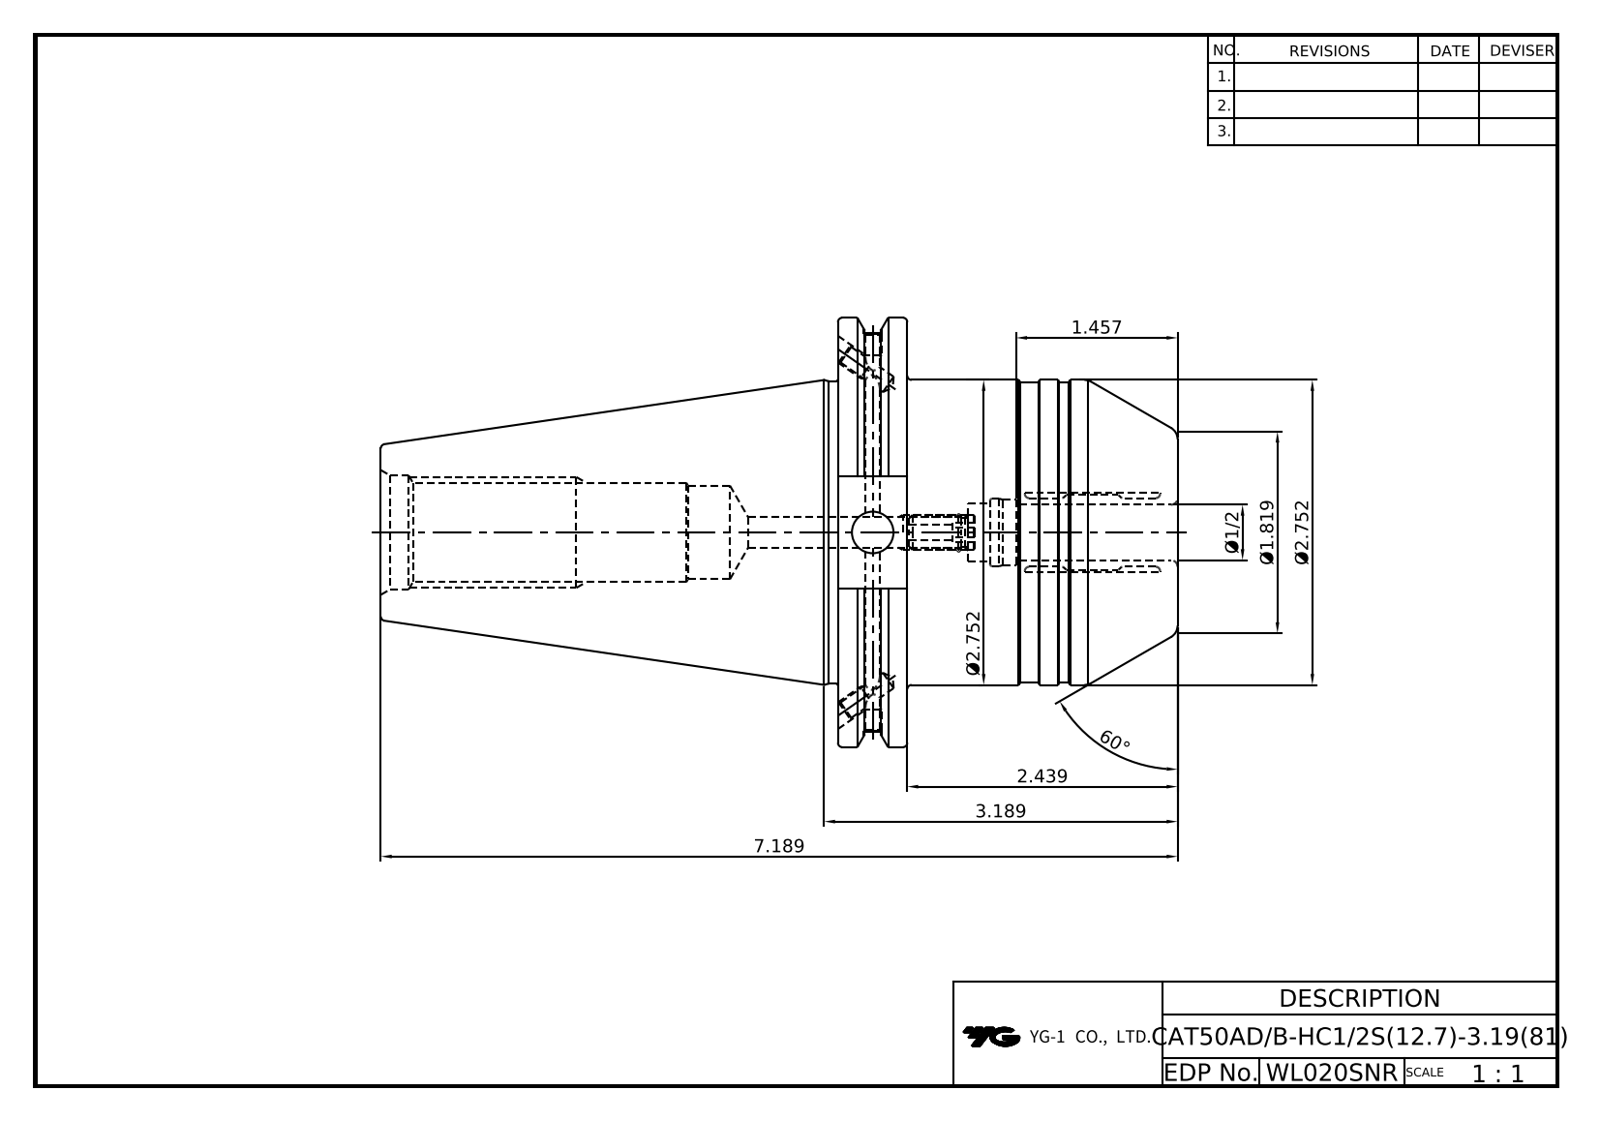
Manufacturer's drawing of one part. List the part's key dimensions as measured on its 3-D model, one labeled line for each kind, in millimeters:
Part name (STEP PRODUCT): LO-CAT50ADB-HC12.7S-81
STEP written by: Autodesk Inventor 2020 (AUTOMOTIVE_DESIGN)
Units: millimetres
Bodies: 1 solid, 102 faces (37 planar, 31 cylindrical, 34 other)
Overall size (bounding box): 182.6 × 98.42 × 94.69
Volume: 537 821 mm³ · Surface area: 57 060 mm²
Round holes (diameter × count): ⌀3.24 ×2, ⌀4.13 ×2, ⌀4.2 ×2, ⌀5 ×2, ⌀6.92 ×1, ⌀9.53 ×1, ⌀12.7 ×1, ⌀13.2 ×1, ⌀21.5 ×1, ⌀21.97 ×1, ⌀26.2 ×1
Round bosses / shafts (diameter × count): ⌀98.42 ×1, ⌀91.29 ×1, ⌀69.9 ×1, ⌀69.25 ×1, ⌀68.9 ×1
Main face-to-face distances: 15.88, 77.83, 61.95, 104.77, 120.65, 182.6, 73.03, 25.9, 110.82, 6.05
